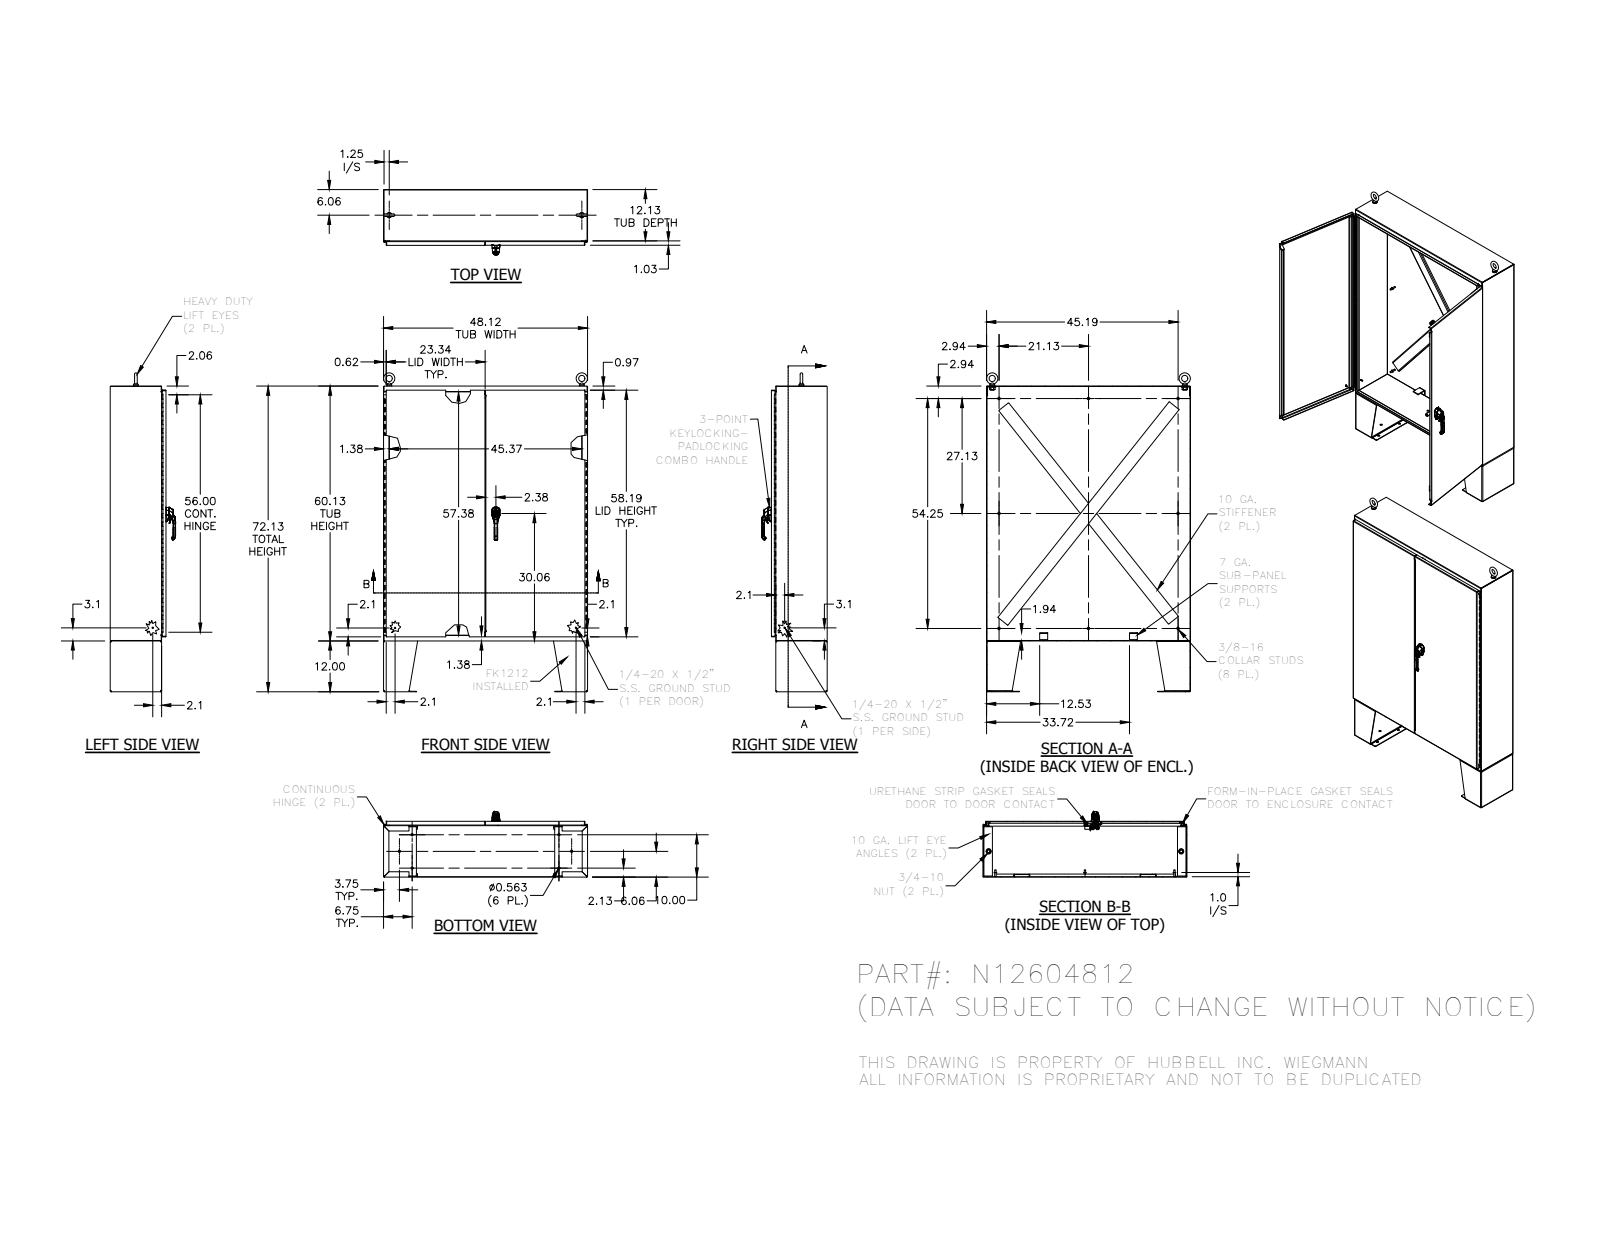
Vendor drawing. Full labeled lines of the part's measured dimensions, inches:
Part name (STEP PRODUCT): N12604812 Correct
STEP written by: SolidWorks 2019 (AUTOMOTIVE_DESIGN)
Units: inches
Bodies: 73 solids, 2287 faces (1331 planar, 734 cylindrical, 222 other)
Overall size (bounding box): 75.344 × 48.139 × 15.449
Volume: 1 206 in³ · Surface area: 22 474 in²
Round holes (diameter × count): ⌀0.563 ×18, ⌀0.277 ×8, ⌀0.375 ×6, ⌀0.375 ×5, ⌀0.2 ×4, ⌀0.28 ×3, ⌀0.187 ×2, ⌀0.241 ×2, ⌀0.25 ×2, ⌀0.252 ×2, ⌀0.4 ×2, ⌀0.45 ×2
Round bosses / shafts (diameter × count): ⌀0.33 ×8, ⌀0.625 ×5, ⌀0.625 ×3, ⌀0.337 ×3, ⌀0.25 ×3, ⌀1.25 ×2, ⌀1 ×2, ⌀0.738 ×2
Partial cylindrical surfaces — rounded edges, fillets, slot ends (radius × count): R0.094 ×38, R0.219 ×22, R0.125 ×19, R0.05 ×18, R0.025 ×16, R0.03 ×16, R0.198 ×15, R0.031 ×9
Main face-to-face distances: 0.104, 13.23, 0.104, 48.021, 13.126, 13.334, 13.239, 13.135, 0.095, 13.344
Hole centre spacings: 12, 47.917, 24, 52.231, 46.391, 2.041, 4.89, 5
